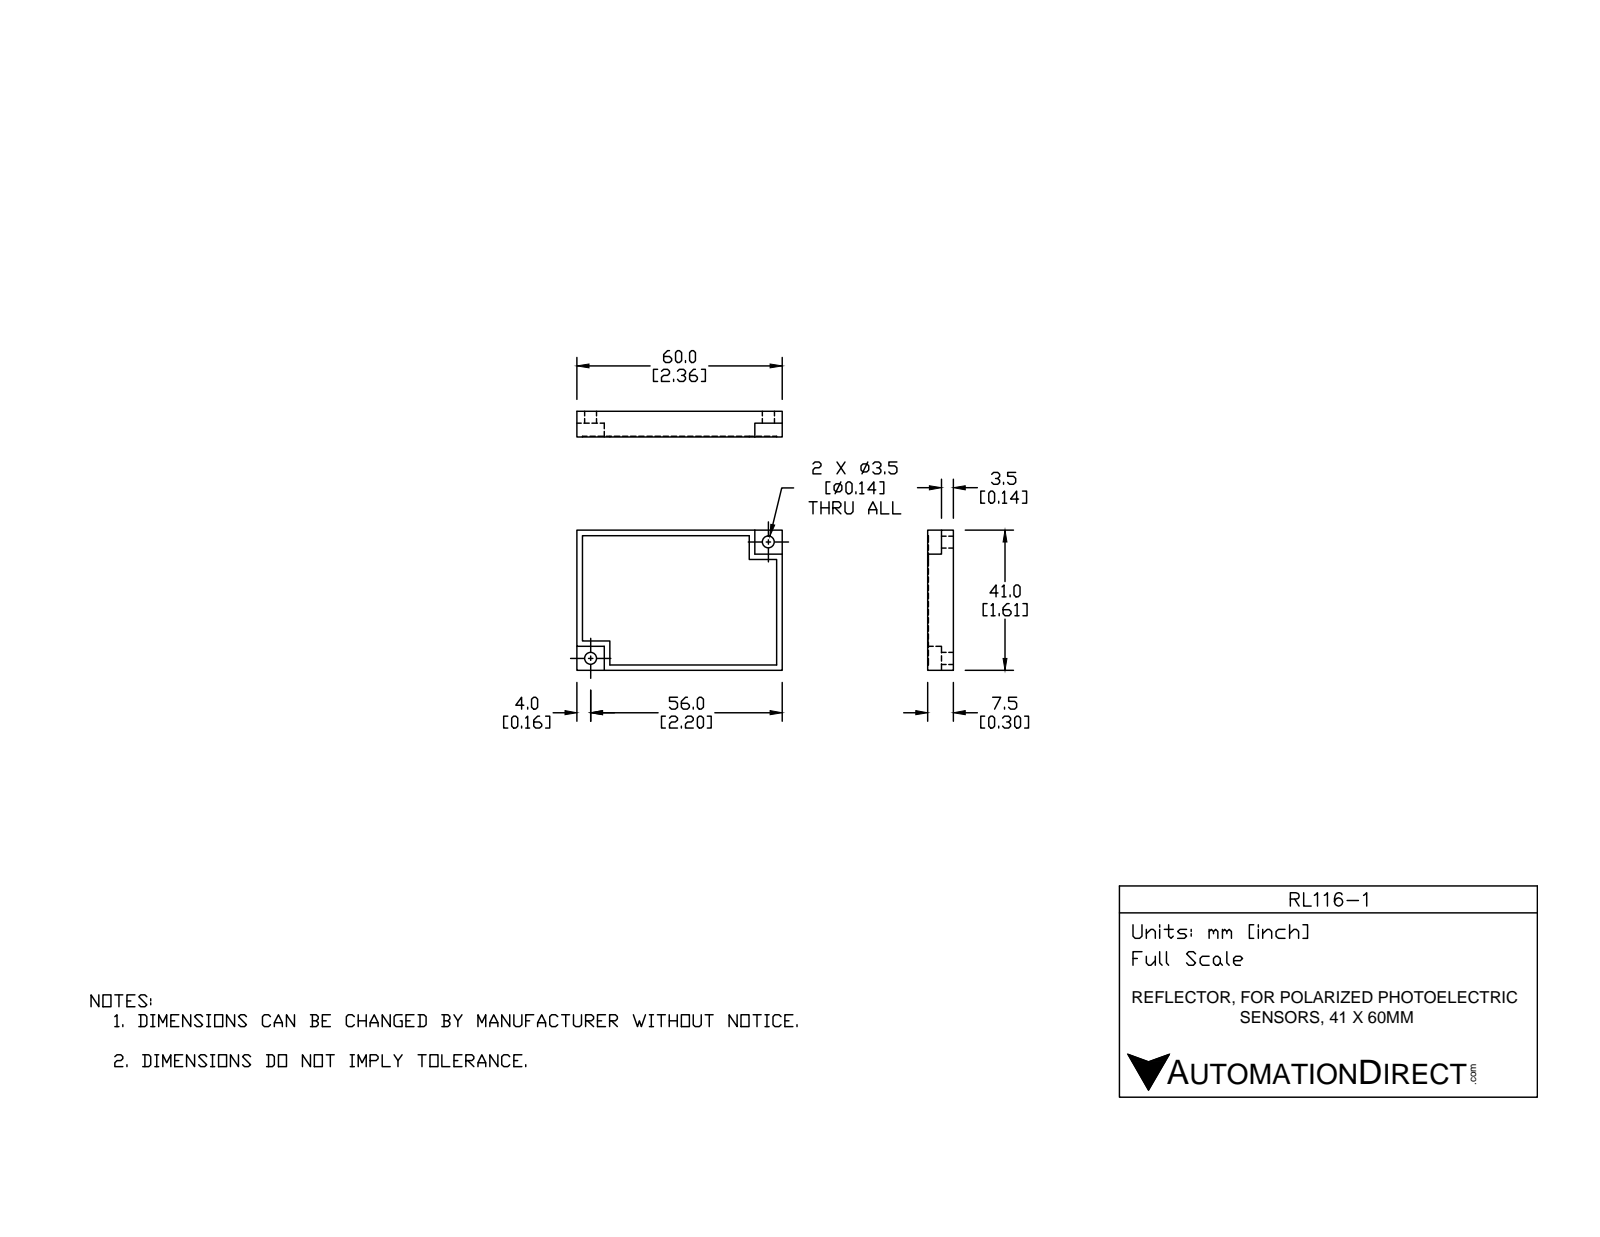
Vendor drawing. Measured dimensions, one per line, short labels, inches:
name: RL-116-1
written by: SolidWorks 2017 (AUTOMOTIVE_DESIGN)
unit: in
bodies: 1 solid, 25 faces (21 planar, 4 cylindrical, 0 other)
size: 2.362 × 1.614 × 0.295
volume: 1.07 in³; area: 10.09 in²
holes: 2× ⌀0.138
face distances: 0.287, 1.614, 0.295, 2.362, 0.138, 0.15, 0.157, 0.276, 1.339, 0.315
hole spacings: 2.446
